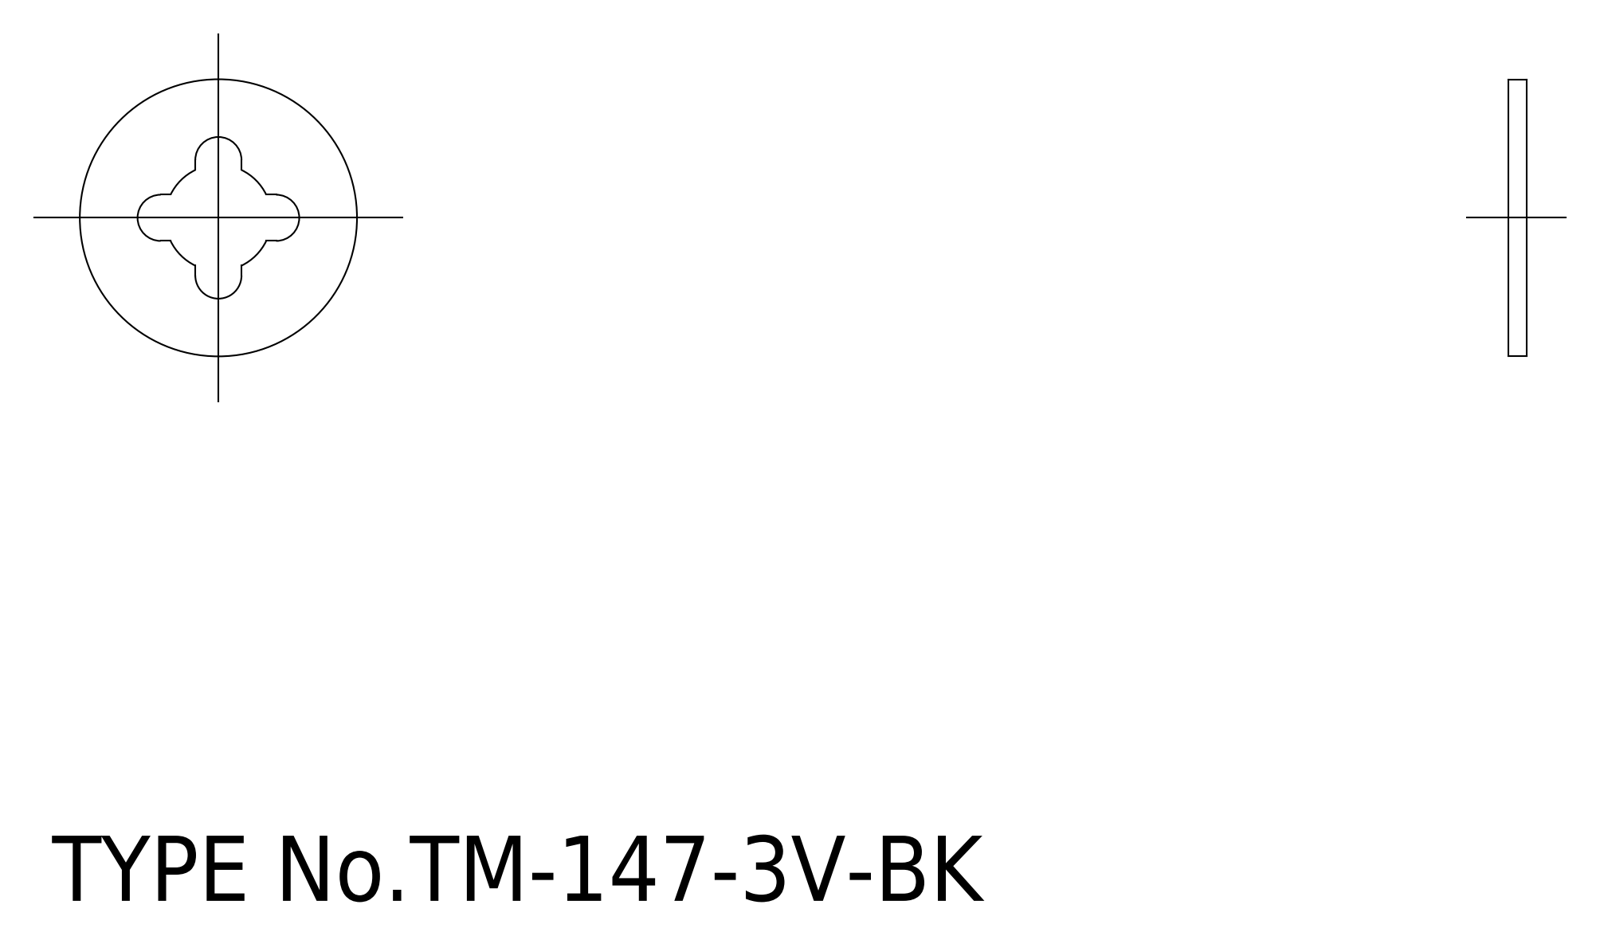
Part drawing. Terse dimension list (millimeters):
written by: spGate 19.8.4 (****-****-****-****) (AUTOMOTIVE_DESIGN)
unit: mm
bodies: 1 solid, 20 faces (10 planar, 10 cylindrical, 0 other)
size: 12 × 12 × 0.8
volume: 70 mm³; area: 224 mm²
bosses: 1× ⌀12
rounds: 4× R1, 1× R2.3
face distances: 0.8, 2
